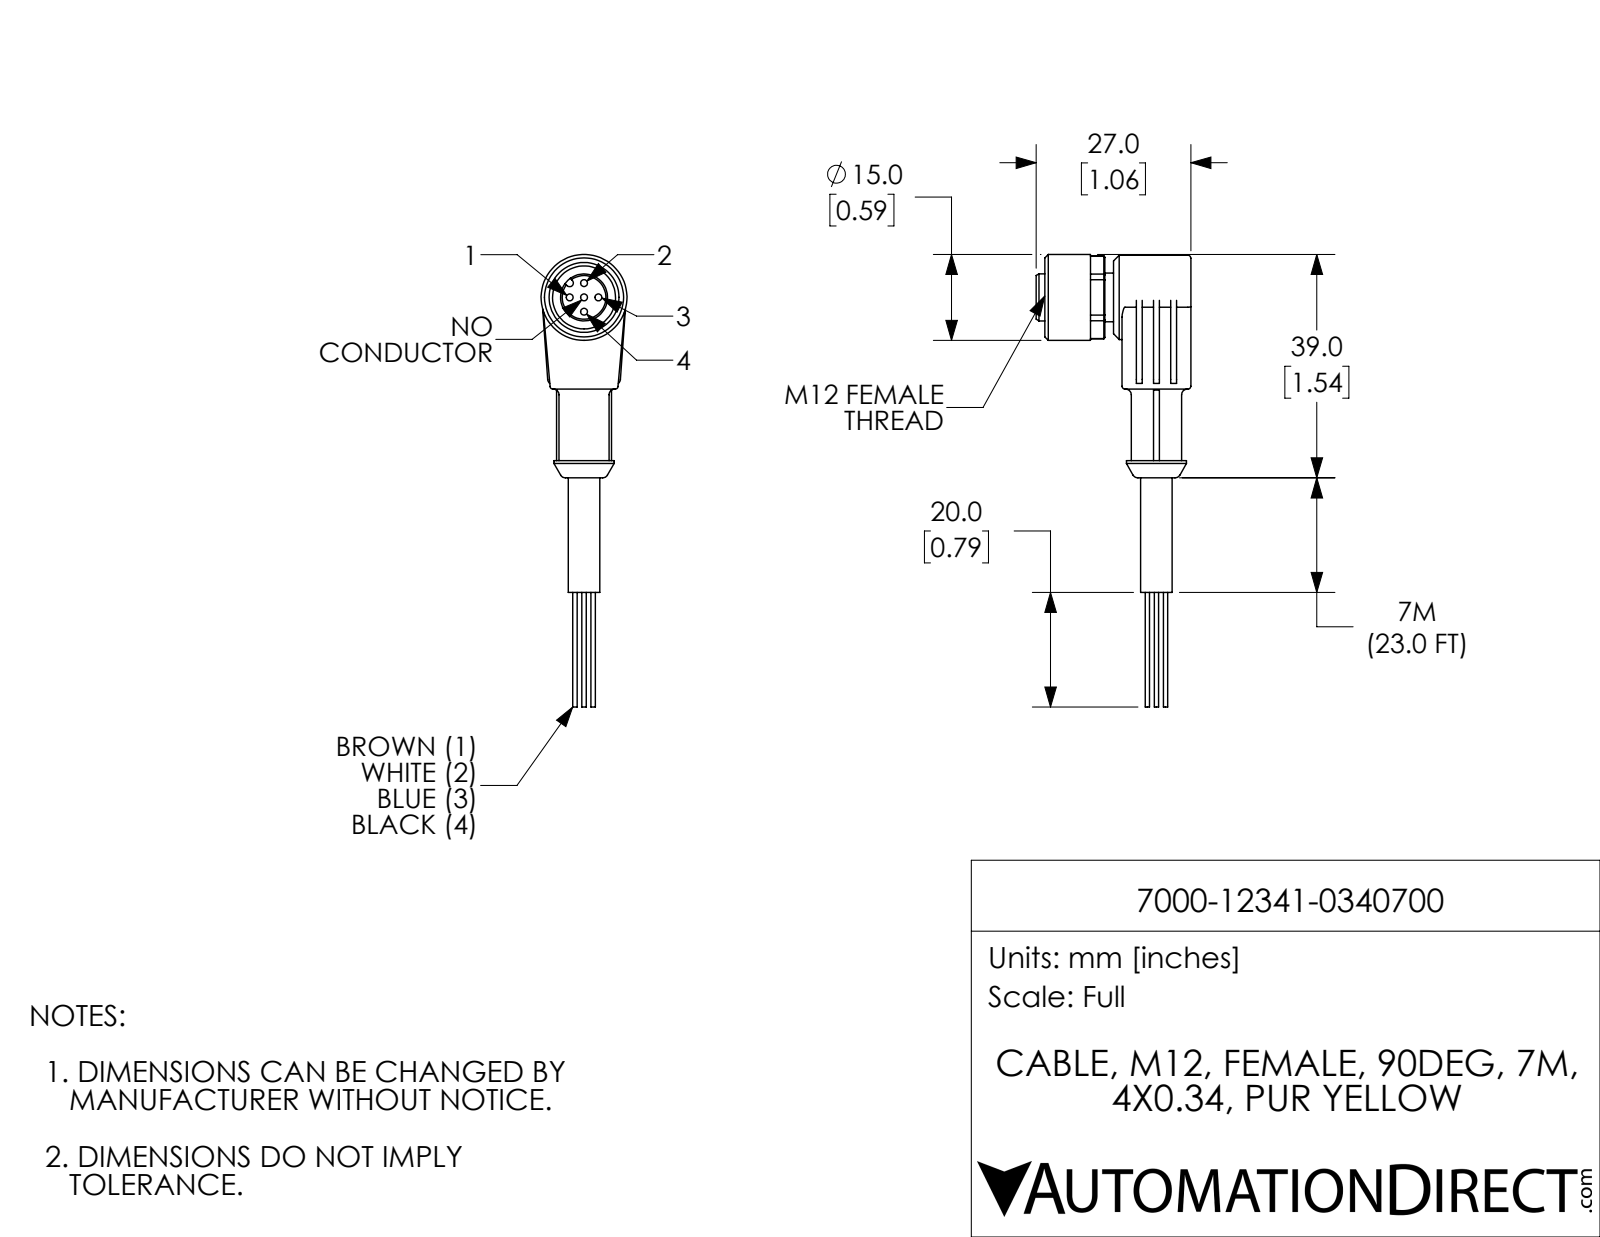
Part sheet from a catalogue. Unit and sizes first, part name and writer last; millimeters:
Units: millimetres
Overall size (bounding box): 79 × 27 × 15
Round holes (diameter × count): ⌀1.2 ×5, ⌀4.8 ×1, ⌀11 ×1
Round bosses / shafts (diameter × count): ⌀0.8 ×4, ⌀15 ×1, ⌀14.7 ×1, ⌀10.5 ×1, ⌀8.8 ×1, ⌀8.5 ×1, ⌀8.2 ×1, ⌀5.5 ×1
Partial cylindrical surfaces — rounded edges, fillets, slot ends (radius × count): R0.5 ×8, R1 ×2, R0.7 ×1, R7.2 ×1
Main face-to-face distances: 12, 1.5, 3, 13.5, 15, 5.5, 9.5, 6, 8, 12.5
Hole centre spacings: 2.5, 3.5, 5
Volume: 6 830 mm³ · Surface area: 3 804 mm²
Bodies: 1 solid, 152 faces (65 planar, 59 cylindrical, 28 other)
Part name (STEP PRODUCT): 7000-12341-0340700
STEP written by: SolidWorks 2021 (CONFIG_CONTROL_DESIGN)
